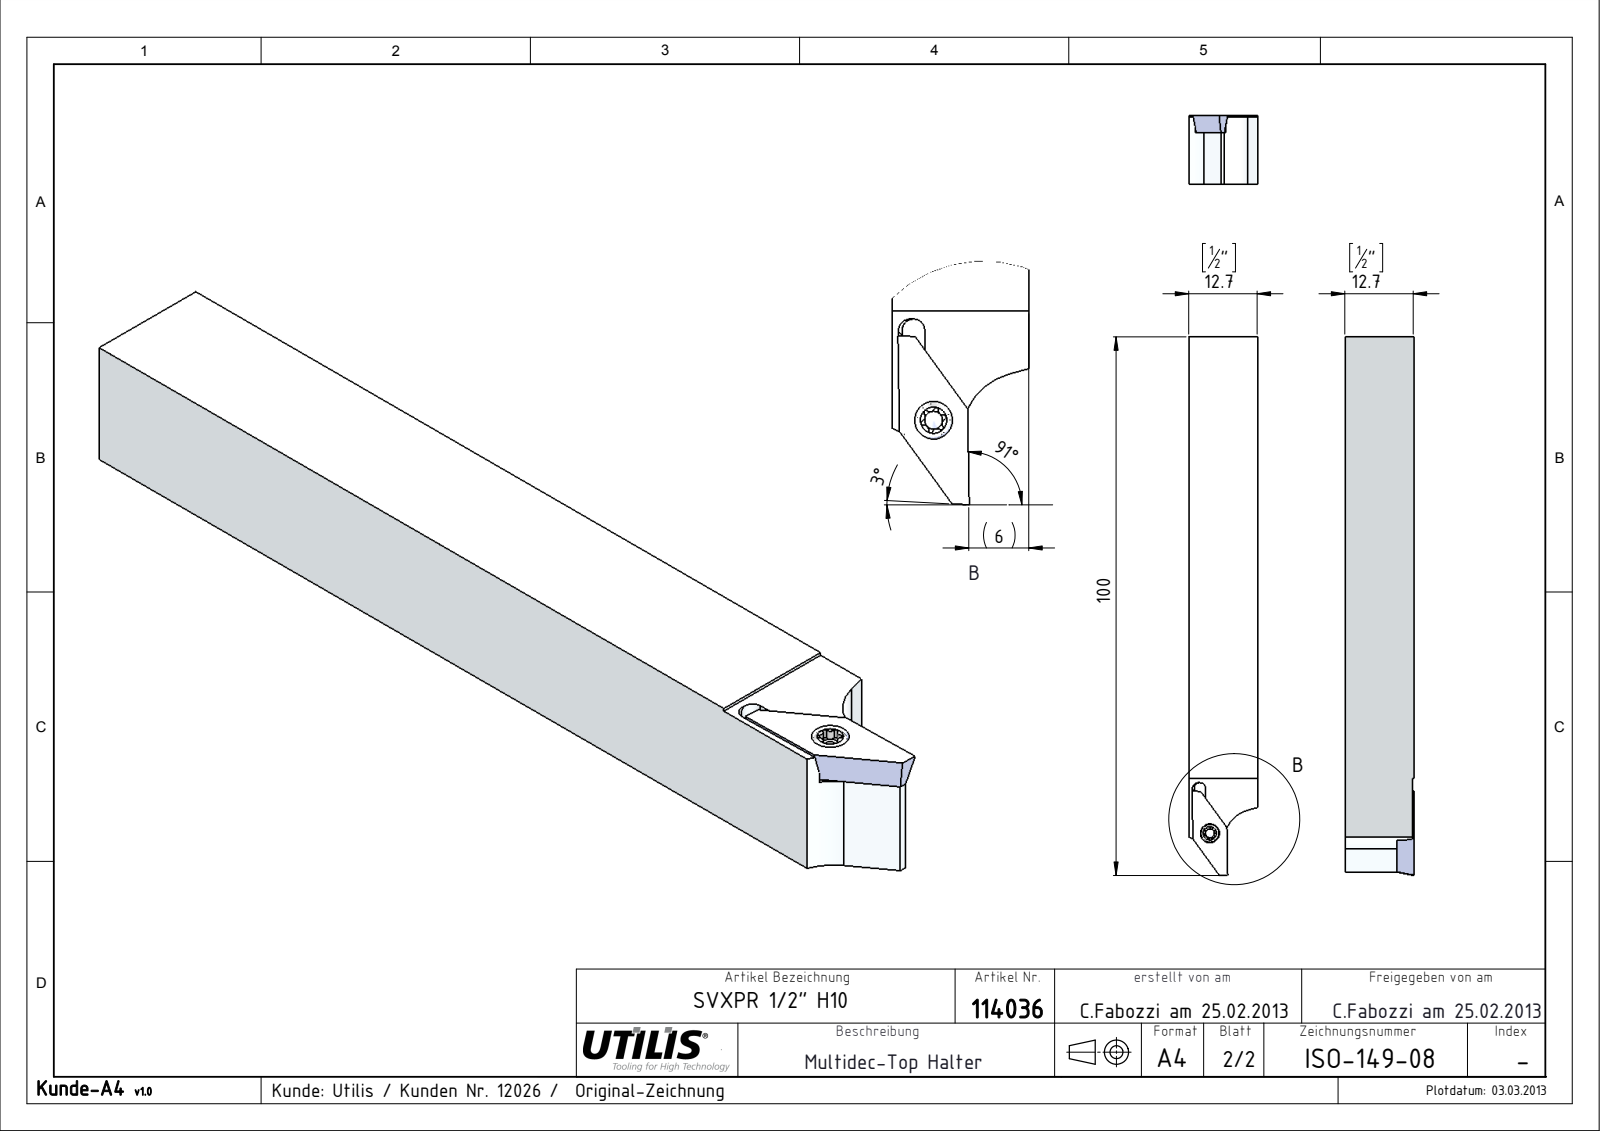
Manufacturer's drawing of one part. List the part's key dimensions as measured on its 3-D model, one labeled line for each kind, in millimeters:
Part name (STEP PRODUCT): VPGT 10 R_VPGT 10 R; ISO-149-Kunde_08; ISO-149-08; MSP-7_M2,5X6-TX8 CERATIZIT Schraube
STEP written by: SolidWorks 2015 (CONFIG_CONTROL_DESIGN)
Units: millimetres
Bodies: 3 solids, 72 faces (28 planar, 27 cylindrical, 17 other)
Overall size (bounding box): 100 × 12.7 × 12.7
Volume: 14 858 mm³ · Surface area: 5 481 mm²
Round holes (diameter × count): ⌀2.05 ×1, ⌀3 ×1
Round bosses / shafts (diameter × count): ⌀3.45 ×1, ⌀2.5 ×1
Partial cylindrical surfaces — rounded edges, fillets, slot ends (radius × count): R0.2 ×6, R0.45 ×6, R6 ×2, R1.05 ×1
Main face-to-face distances: 12.7, 9.52, 3.18, 12.4, 2.88, 5.33, 2.1, 3.23, 5.32, 82
